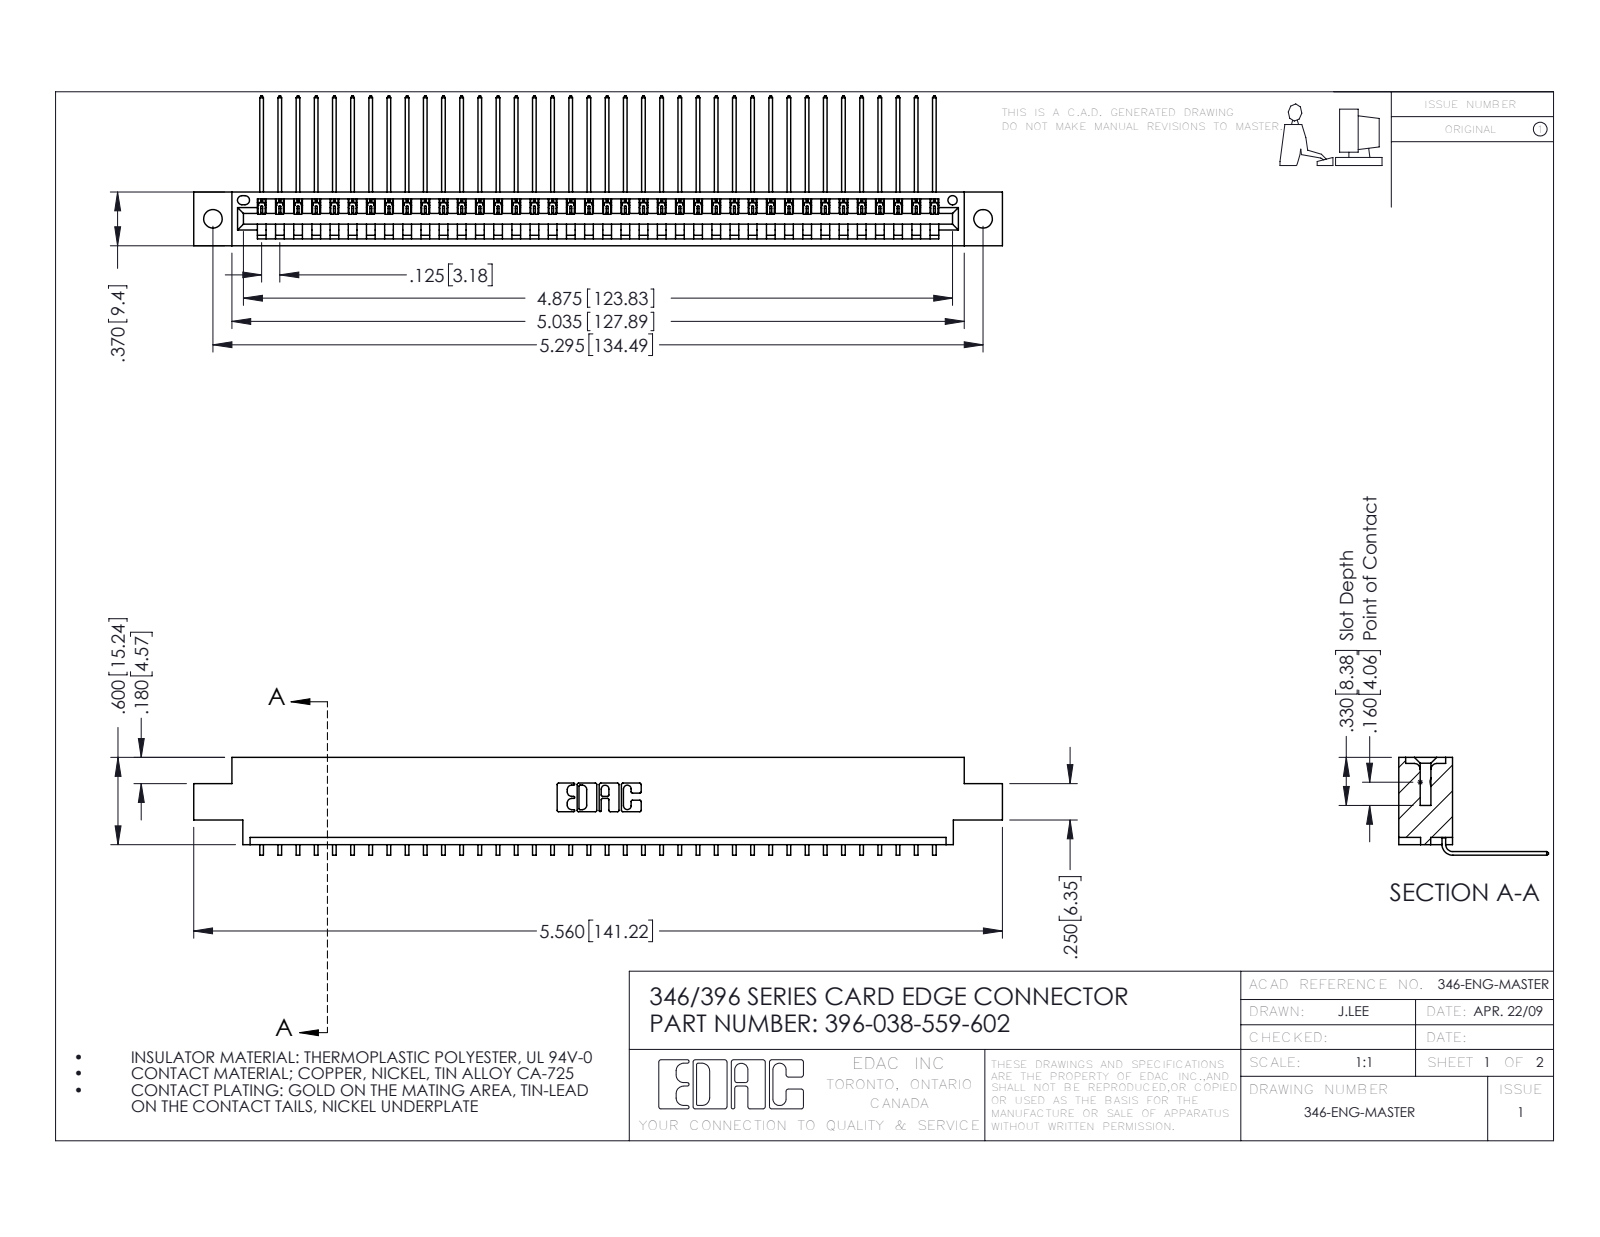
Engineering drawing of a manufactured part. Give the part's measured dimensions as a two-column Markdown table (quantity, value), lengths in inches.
| quantity | value |
| --- | --- |
| part name | 396-038-559-602; 345-292-001_558 559 Tail - 1; 346 Part_0.170 Offset - 0.128 Dia |
| STEP written by | SolidWorks 2016 (CONFIG_CONTROL_DESIGN) |
| units | inches |
| bodies | 39 solids, 2406 faces (1676 planar, 730 cylindrical, 0 other) |
| overall size | 5.56 × 1.03 × 0.673 |
| volume | 0.819 in³ |
| surface area | 26.94 in² |
| round holes (diameter × count) | 0.128 × 2, 0.064 × 1 |
| partial cylindrical surfaces (radius × count) | 0.006 × 76, 0.01 × 22, 0.007 × 6, 0.031 × 6, 0.026 × 3, 0.031 × 2, 0.04 × 2, 0.014 × 1 |
| main face-to-face distances | 0.048, 0.322, 0.37, 0.25, 0.025, 0.072, 0.298, 0.148, 0.222, 0.1 |
| hole center spacings | 0.246, 5.086, 5.295 |
